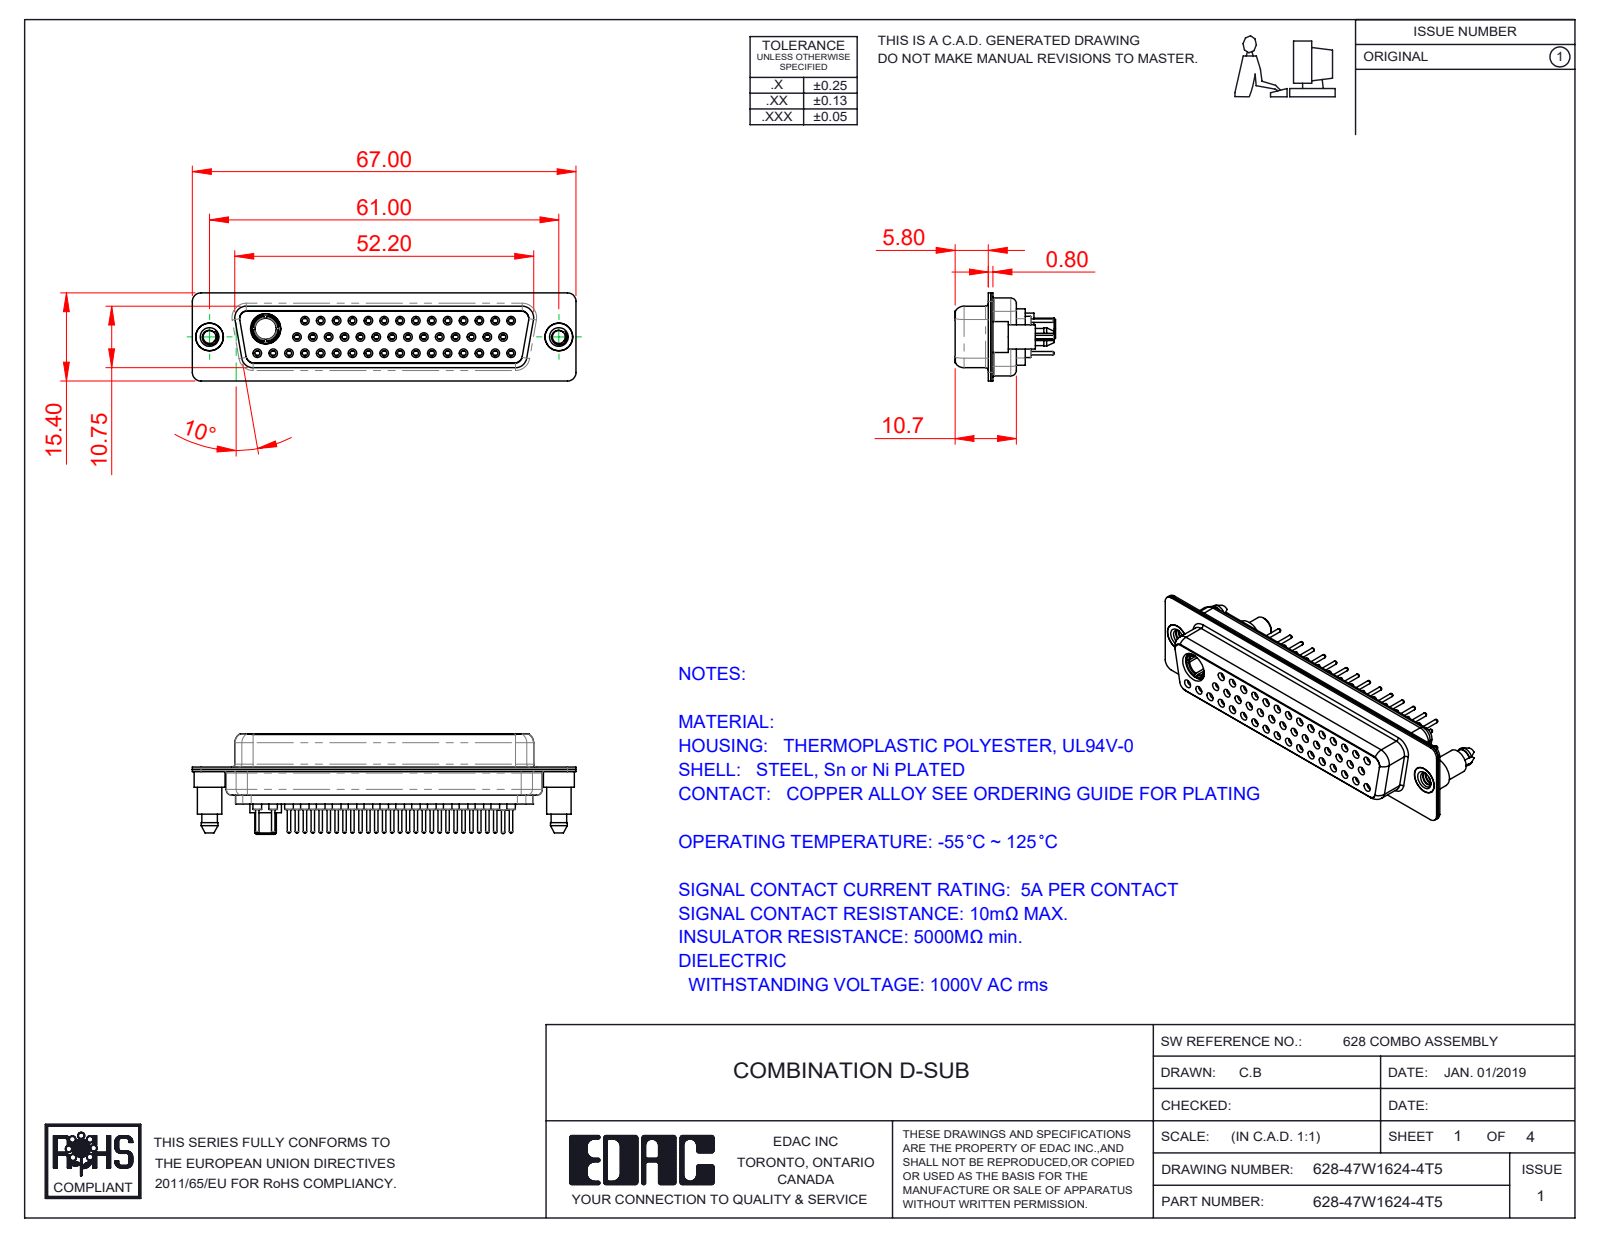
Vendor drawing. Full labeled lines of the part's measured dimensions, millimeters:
Part name (STEP PRODUCT): 628Combo Shell Front_50 Contacts; 628Combo Housing_47W1; 628Combo Contact Row 3_24; 628Combo Threaded Boardlock_5 (+5 more)
STEP written by: SolidWorks 2016 (CONFIG_CONTROL_DESIGN)
Units: millimetres
Bodies: 53 solids, 2921 faces (799 planar, 1058 cylindrical, 1064 other)
Overall size (bounding box): 67 × 17.55 × 15.4
Volume: 7 238 mm³ · Surface area: 15 034 mm²
Round holes (diameter × count): ⌀1.1 ×46, ⌀0.9 ×45, ⌀1.5 ×45, ⌀2 ×45, ⌀1.6 ×31, ⌀1.7 ×14, ⌀4.85 ×3, ⌀2.26 ×2, ⌀4 ×2, ⌀4.05 ×2, ⌀3.7 ×1, ⌀5.3 ×1
Round bosses / shafts (diameter × count): ⌀2.2 ×46, ⌀0.6 ×46, ⌀1.6 ×15, ⌀5.4 ×2, ⌀4.95 ×2, ⌀4.8 ×2, ⌀4.25 ×2, ⌀5.5 ×1
Partial cylindrical surfaces — rounded edges, fillets, slot ends (radius × count): R1.5 ×18, R1.35 ×12, R2 ×12, R1.6 ×10, R0.25 ×4, R0.5 ×4, R0.6 ×4, R0.65 ×4
Main face-to-face distances: 0.4, 11.33, 6.45, 6.05, 1.87, 12.25, 6.2, 5.8, 10.35, 10.93
Hole centre spacings: 3.16, 2.77, 5.54, 8.31, 11.08, 13.85, 16.62, 19.39
